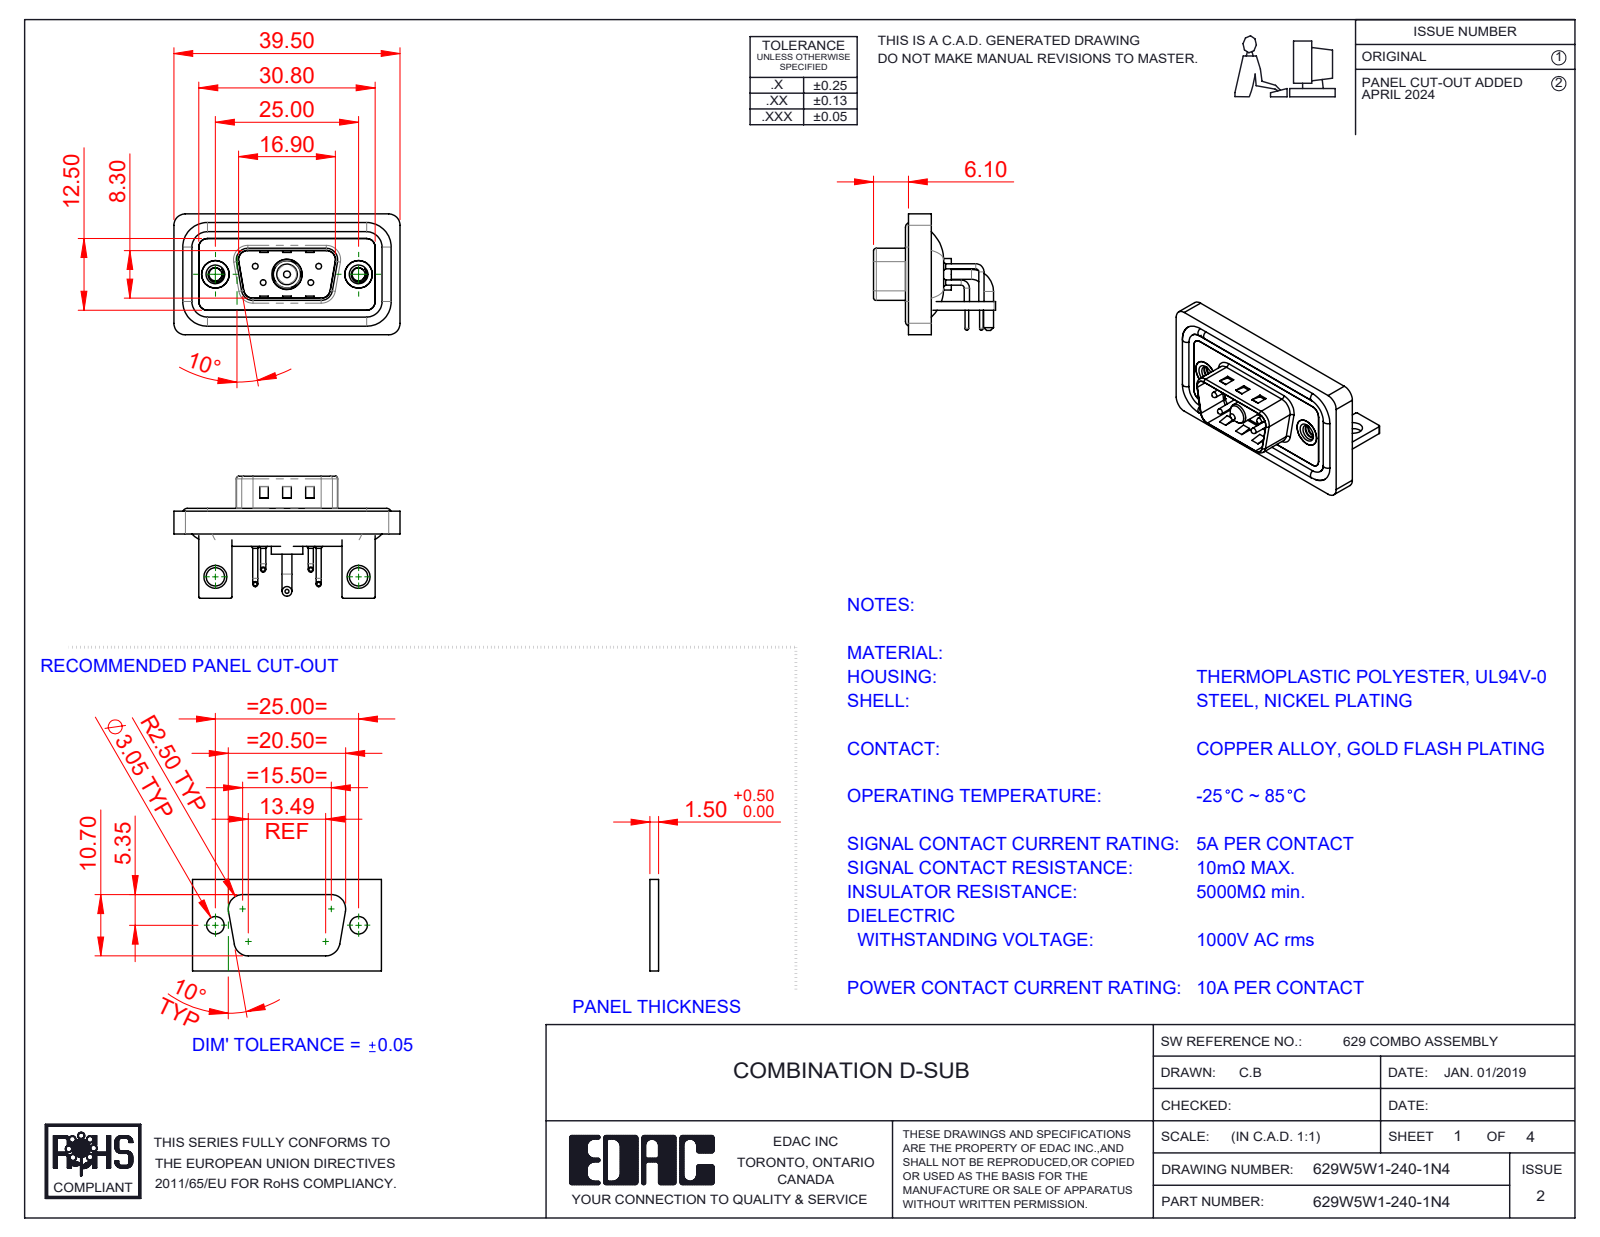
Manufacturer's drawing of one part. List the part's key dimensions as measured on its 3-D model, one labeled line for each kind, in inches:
Part name (STEP PRODUCT): Power Pin_10A RA; 629Combo Contact Row 1; 629Combo Shell Front_09 Contacts; 629W5W1-140-1N4 (+6 more)
STEP written by: SolidWorks 2023 (CONFIG_CONTROL_DESIGN)
Units: inches
Bodies: 15 solids, 934 faces (431 planar, 363 cylindrical, 140 other)
Overall size (bounding box): 1.555 × 0.839 × 0.831
Volume: 0.287 in³ · Surface area: 11.94 in²
Round holes (diameter × count): ⌀0.03 ×4, ⌀0.063 ×4, ⌀0.079 ×4, ⌀0.089 ×2, ⌀0.126 ×2, ⌀0.157 ×2, ⌀0.189 ×2, ⌀0.197 ×2, ⌀0.191 ×1, ⌀0.209 ×1
Round bosses / shafts (diameter × count): ⌀0.035 ×8, ⌀0.063 ×4, ⌀0.059 ×4, ⌀0.039 ×4, ⌀0.026 ×4, ⌀0.193 ×2, ⌀0.067 ×2, ⌀0.217 ×1
Partial cylindrical surfaces — rounded edges, fillets, slot ends (radius × count): R0.079 ×19, R0.059 ×18, R0.01 ×16, R0.02 ×9, R0.063 ×8, R0.024 ×4, R0.026 ×4, R0.035 ×4
Main face-to-face distances: 0.016, 0.059, 0.031, 0.114, 0.043, 0.083, 0.047, 0.063, 0.098, 0.146
Hole centre spacings: 0.124, 0.225, 0.28, 0.492, 0.713, 0.984, 0.173, 0.173
